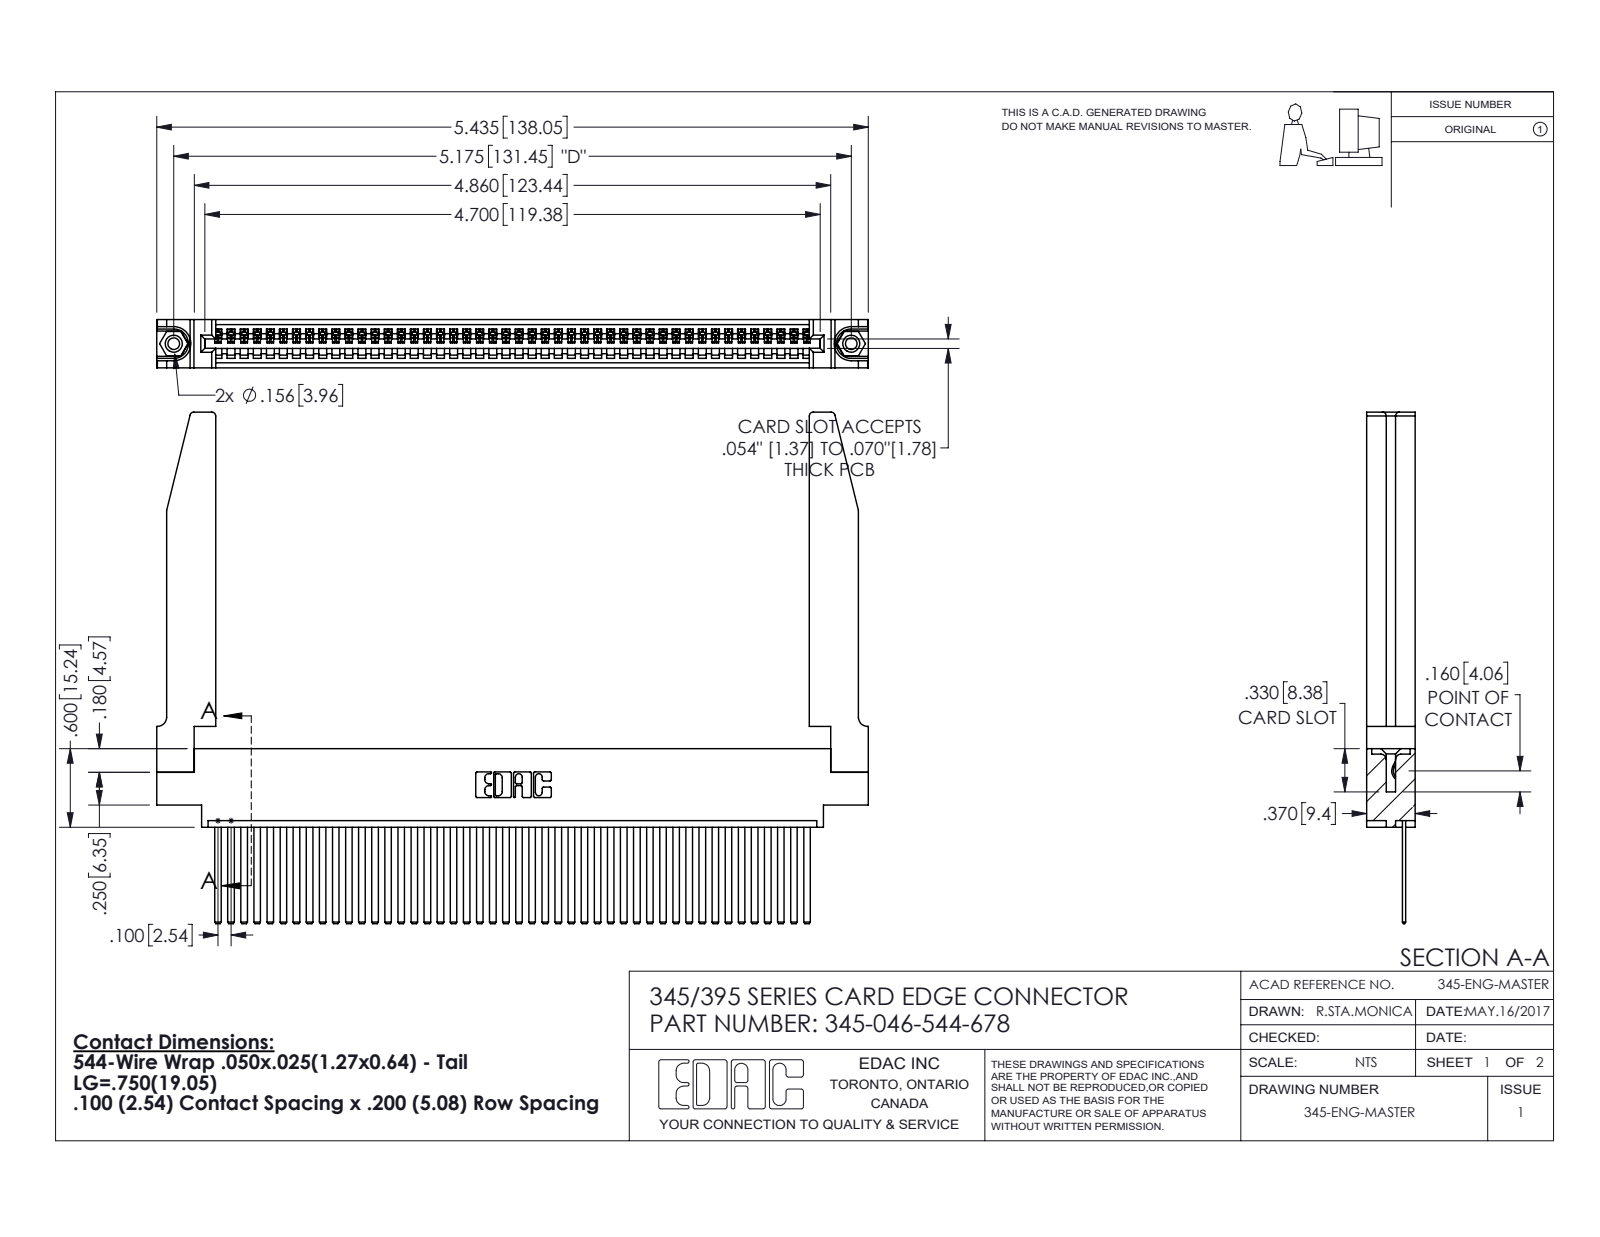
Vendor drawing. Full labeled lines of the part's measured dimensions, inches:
Part name (STEP PRODUCT): 345-250-001_345-250-001-102; 345-220-078_345-220-078; 345-292-001_345-293-144; 345-046-544-678 (+1 more)
STEP written by: SolidWorks 2016 (CONFIG_CONTROL_DESIGN)
Units: inches
Bodies: 51 solids, 2756 faces (1882 planar, 822 cylindrical, 52 other)
Overall size (bounding box): 5.436 × 3.907 × 0.37
Volume: 1.302 in³ · Surface area: 41.31 in²
Round holes (diameter × count): ⌀0.089 ×2, ⌀0.125 ×2, ⌀0.156 ×2, ⌀0.064 ×1
Round bosses / shafts (diameter × count): ⌀0.155 ×2
Partial cylindrical surfaces — rounded edges, fillets, slot ends (radius × count): R0.006 ×92, R0.01 ×22, R0.03 ×8, R0.007 ×6, R0.031 ×6, R0.026 ×3, R0.031 ×2, R0.04 ×2
Main face-to-face distances: 0.072, 0.298, 0.37, 0.098, 0.272, 0.025, 0.2, 0.225, 0.148, 0.15
Hole centre spacings: 0.27, 4.939, 5.175
